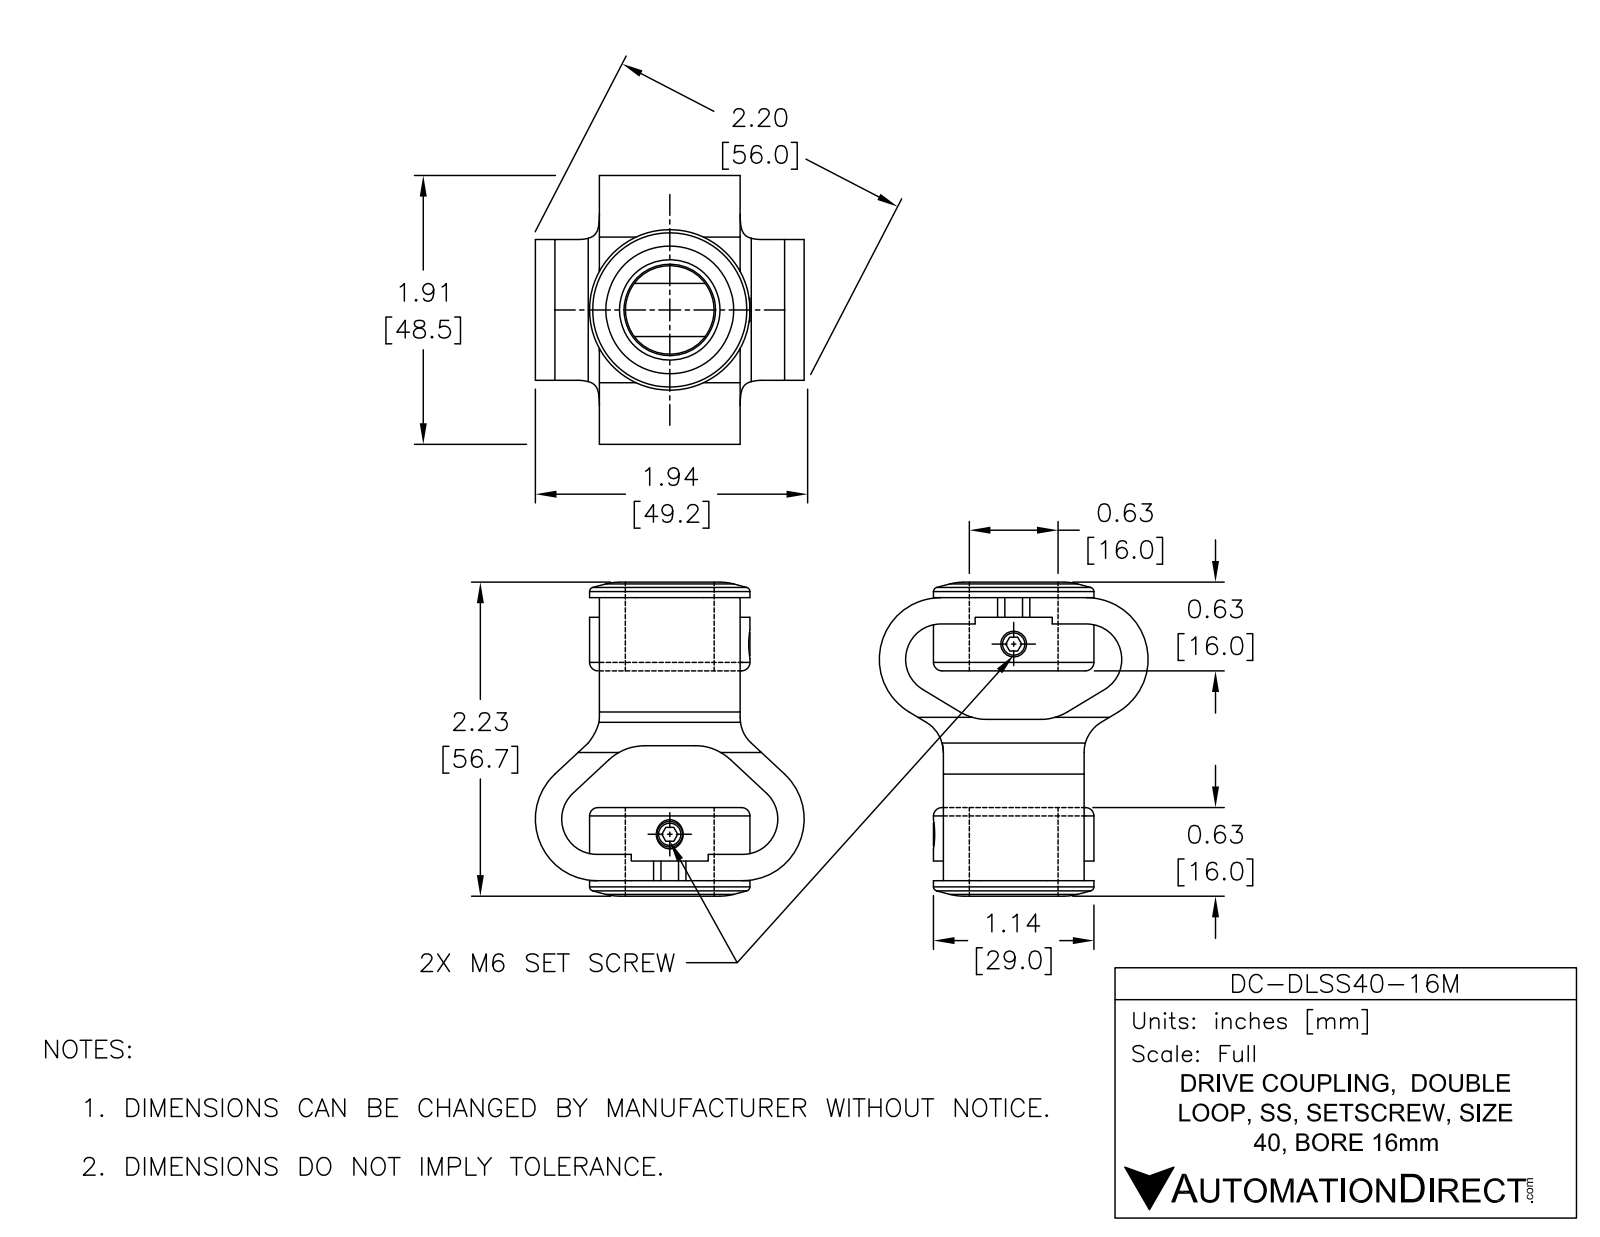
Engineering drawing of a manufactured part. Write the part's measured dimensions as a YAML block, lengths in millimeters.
part_name: "DC-DLSS40-16M"
step_written_by: "SolidWorks 2015 (AUTOMOTIVE_DESIGN)"
units: millimeters
bodies: {solids: 1, faces: 187, planar: 90, cylindrical: 49, other: 48}
overall_size: [56.67, 48.51, 48.51]
volume: 32150
surface_area: 15071
round_holes:
  - {diameter: 4.14, count: 2}
  - {diameter: 16, count: 1}
round_bosses_or_shafts:
  - {diameter: 28.96, count: 1}
partial_cylinders:
  - {radius: 6.35, count: 8}
  - {radius: 6.36, count: 4}
  - {radius: 9.53, count: 4}
  - {radius: 11.11, count: 3}
  - {radius: 10.41, count: 1}
  - {radius: 11.11, count: 1}
face_to_face_distances: [25.4, 4.75, 24.67, 15.9, 8.77, 11.15, 13.52, 21.98, 24.35, 4.76]
